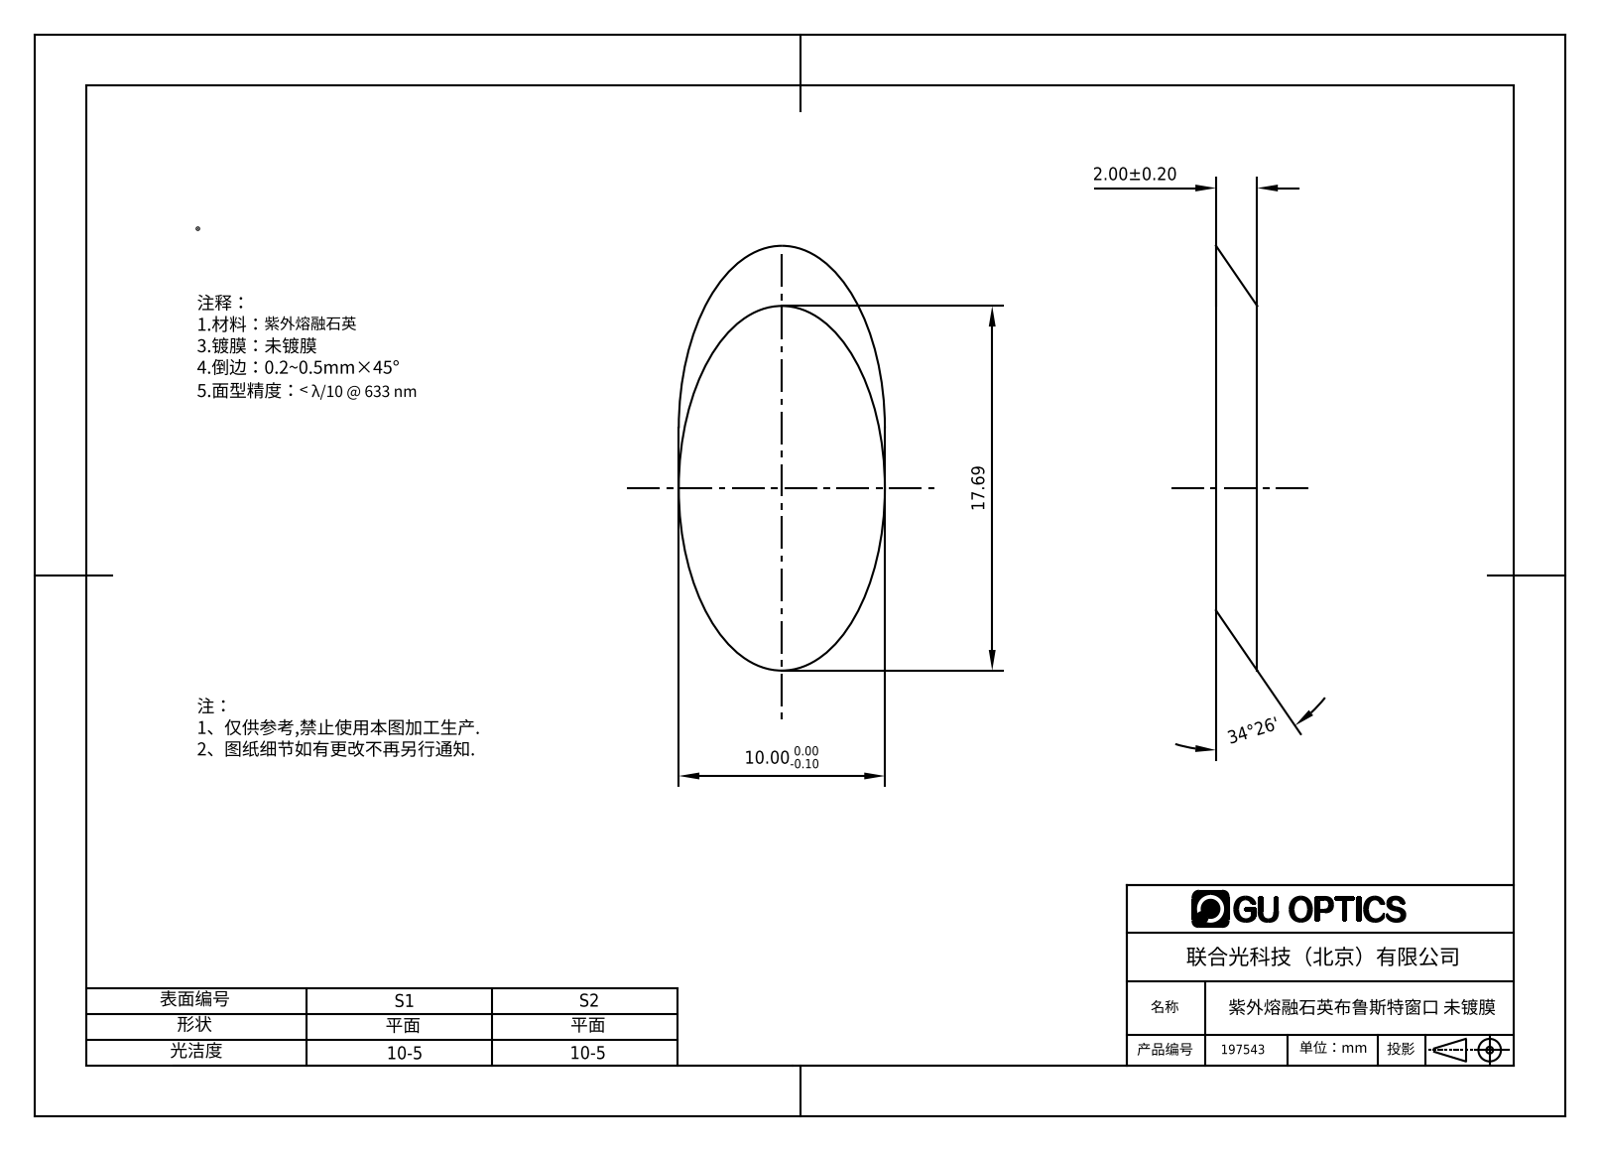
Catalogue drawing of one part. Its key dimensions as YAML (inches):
part_name: "Web Model 65823"
step_written_by: "SolidWorks 2016 (CONFIG_CONTROL_DESIGN)"
units: inches
bodies: {solids: 1, faces: 4, planar: 2, cylindrical: 2, other: 0}
overall_size: [0.811, 0.394, 0.079]
volume: 0.017
surface_area: 0.603
round_bosses_or_shafts:
  - {diameter: 0.394, count: 1}
face_to_face_distances: [0.079]
